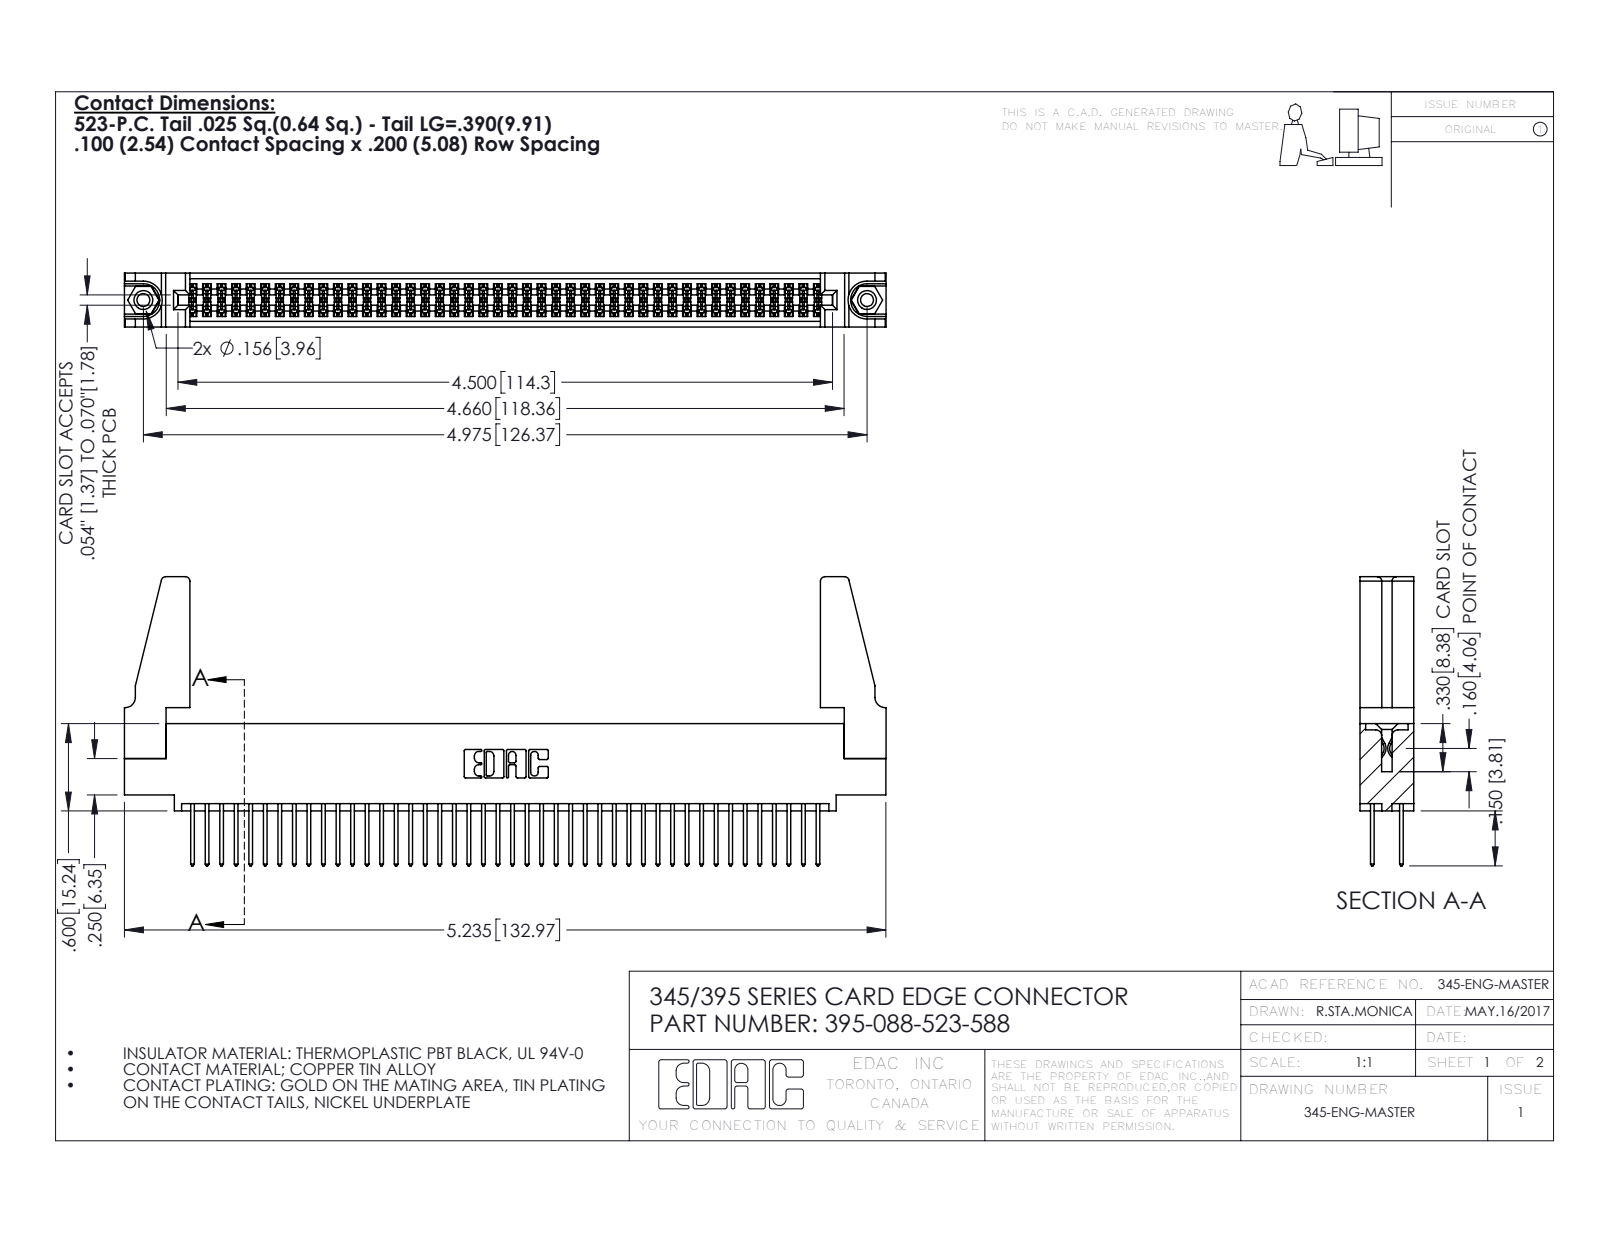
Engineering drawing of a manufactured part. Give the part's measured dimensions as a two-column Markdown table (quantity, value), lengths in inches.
| quantity | value |
| --- | --- |
| part name | 395-088-523-588; 345-292-001_345-293-123; 345-220-078_345-220-088; 345-250-001_345-250-001-102 (+1 more) |
| STEP written by | SolidWorks 2016 (CONFIG_CONTROL_DESIGN) |
| units | inches |
| bodies | 93 solids, 4654 faces (3060 planar, 1578 cylindrical, 16 other) |
| overall size | 5.236 × 1.987 × 0.37 |
| volume | 0.995 in³ |
| surface area | 36.19 in² |
| round holes (diameter × count) | 0.089 × 2, 0.125 × 2, 0.156 × 2, 0.064 × 1 |
| round bosses / shafts (diameter × count) | 0.155 × 2 |
| partial cylindrical surfaces (radius × count) | 0.006 × 132, 0.01 × 88, 0.01 × 22, 0.03 × 8, 0.007 × 6, 0.031 × 6, 0.026 × 3, 0.014 × 2 |
| main face-to-face distances | 0.072, 0.298, 0.37, 0.2, 0.098, 0.272, 0.025, 0.225, 0.175, 0.149 |
| hole center spacings | 0.27, 4.739, 4.975 |
